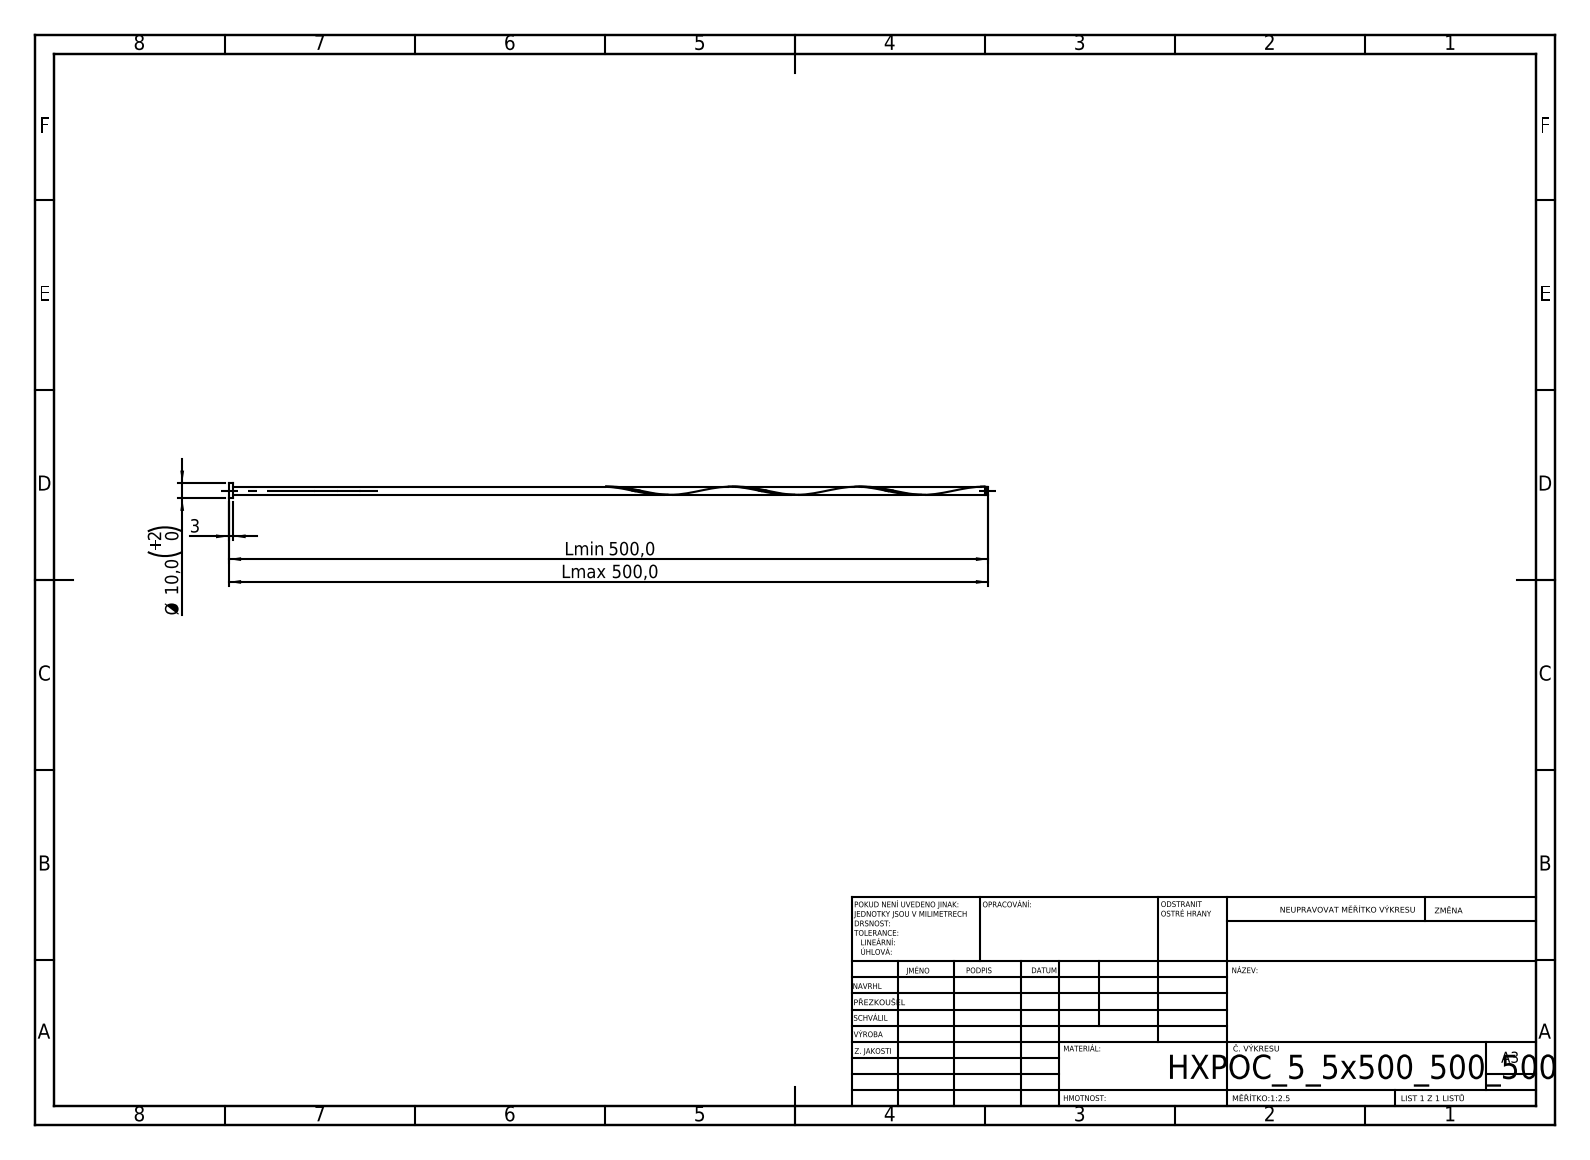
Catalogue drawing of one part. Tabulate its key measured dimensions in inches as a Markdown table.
| quantity | value |
| --- | --- |
| STEP written by | SolidWorks 2019 (CONFIG_CONTROL_DESIGN) |
| units | inches |
| bodies | 1 solid, 16 faces (6 planar, 9 cylindrical, 1 other) |
| overall size | 19.685 × 0.394 × 0.394 |
| volume | 0.889 in³ |
| surface area | 18.39 in² |
| round bosses / shafts (diameter × count) | 0.394 × 1, 0.217 × 1, 0.173 × 1 |
| main face-to-face distances | 0.118, 19.685, 19.567, 19.643, 19.524, 0.043, 19.599, 19.481, 0.043, 0.086 |
